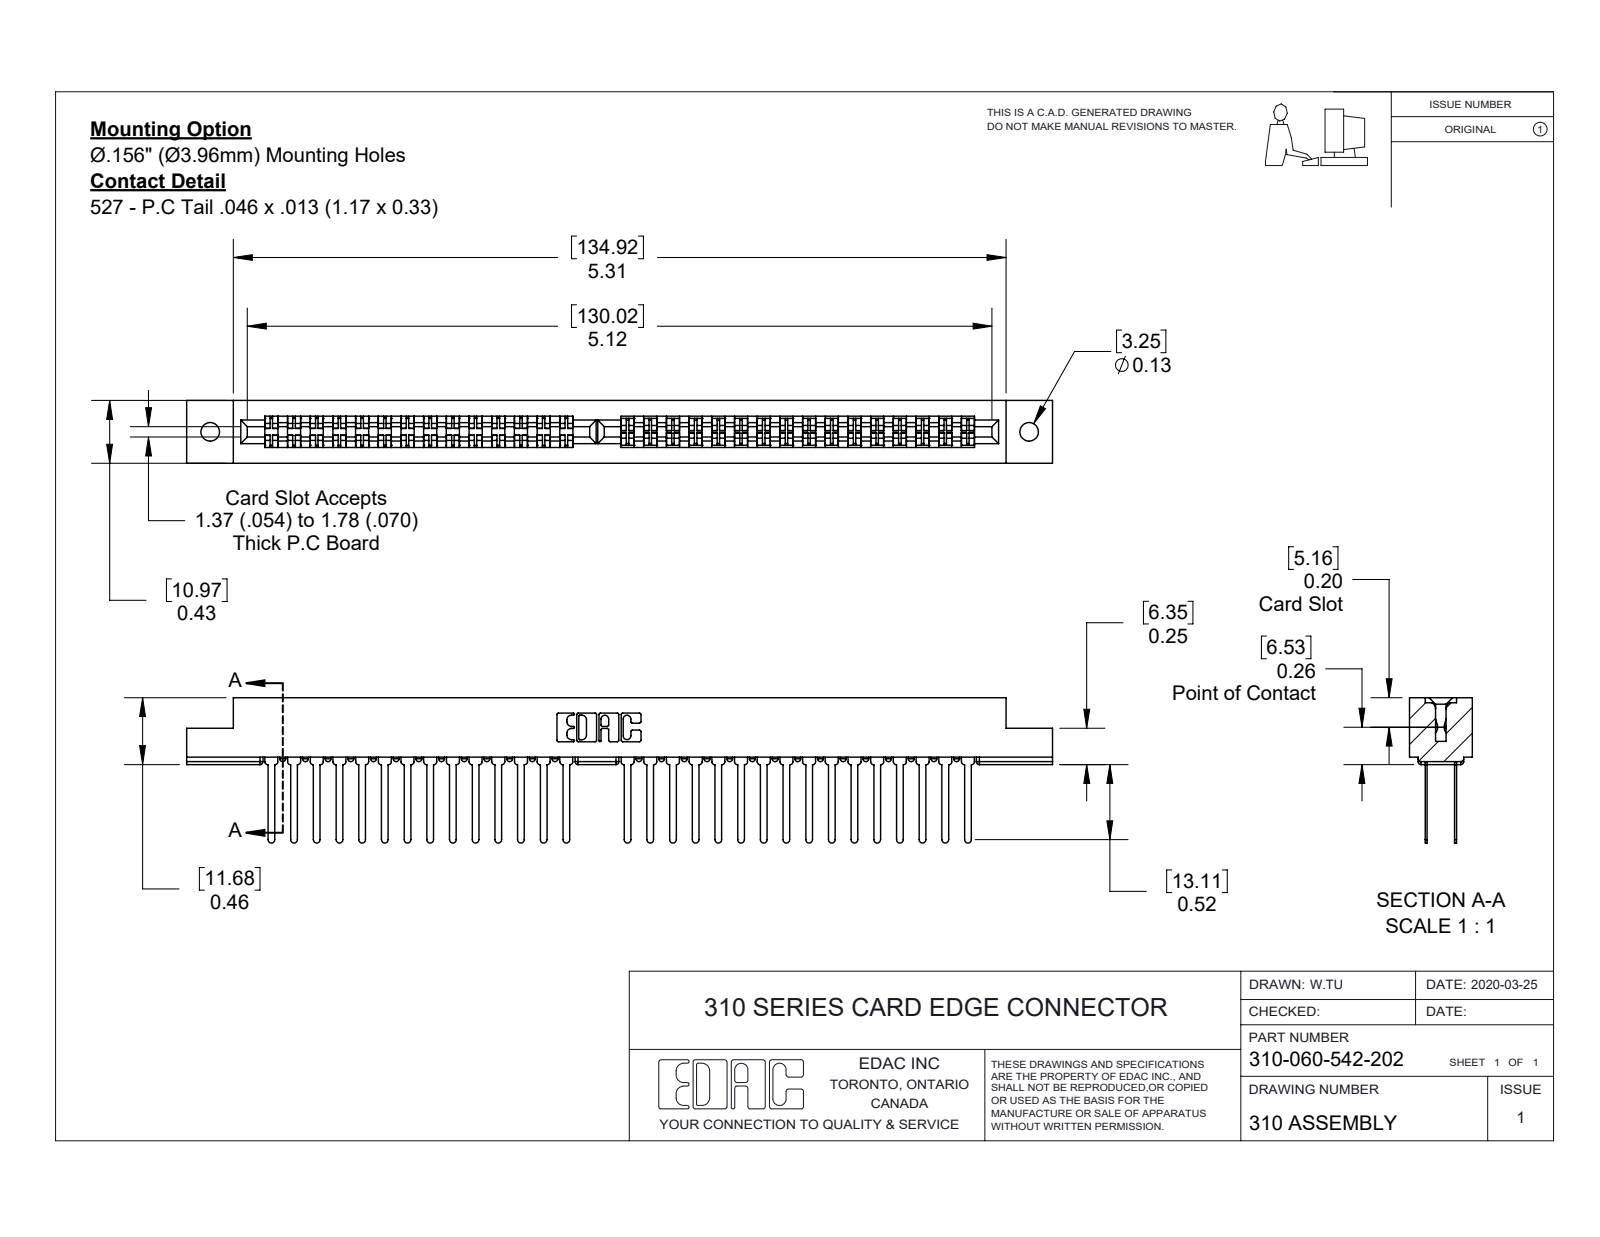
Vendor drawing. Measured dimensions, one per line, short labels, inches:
name: 307-290-001_542; 310 Part_.128 Dia. Hole; 310-060-542-202
written by: SolidWorks 2016 (CONFIG_CONTROL_DESIGN)
unit: in
bodies: 61 solids, 2926 faces (1944 planar, 918 cylindrical, 64 other)
size: 5.953 × 0.999 × 0.432
volume: 0.806 in³; area: 29.53 in²
holes: 2× ⌀0.128
rounds: 158× R0.02, 30× R0.023, 22× R0.01, 6× R0.007, 6× R0.031, 4× R0.012, 4× R0.025, 4× R0.047
face distances: 0.109, 0.013, 0.324, 0.015, 0.187, 0.432, 0.124, 0.309, 0.2, 0.215
hole spacings: 5.63
